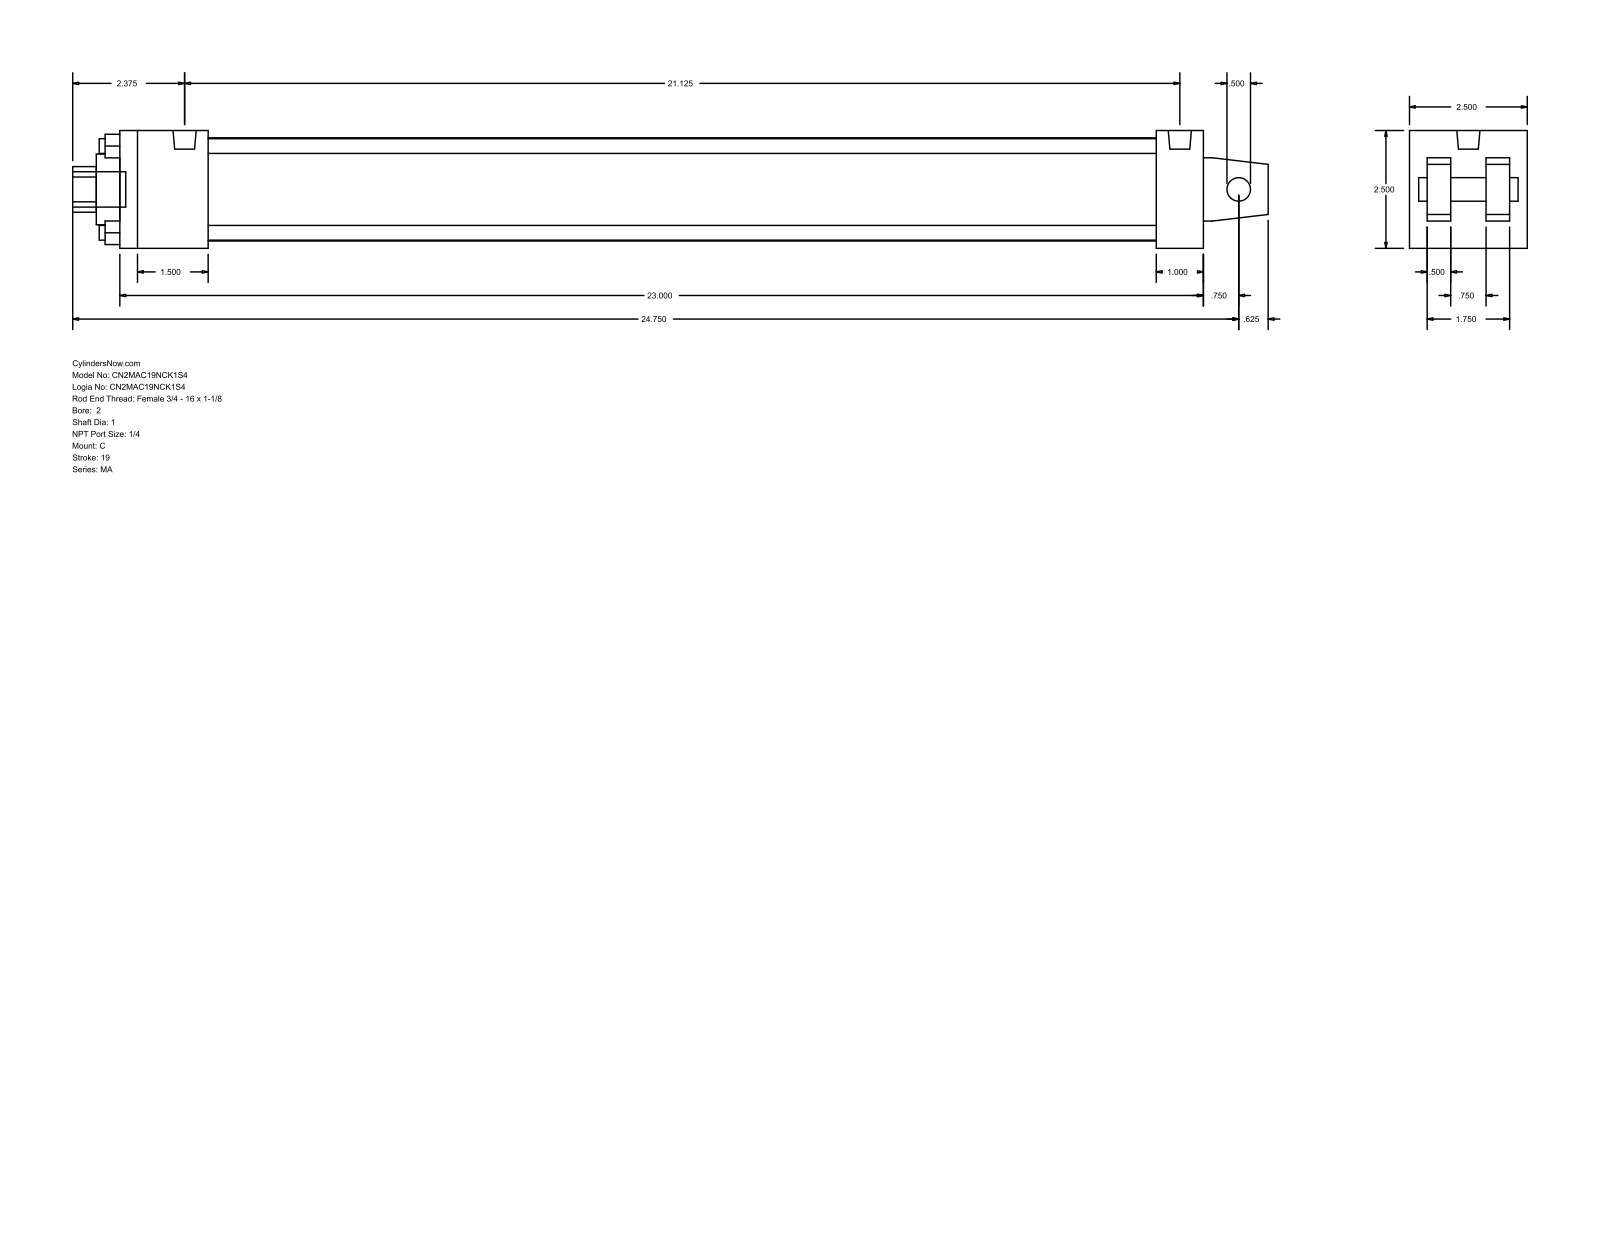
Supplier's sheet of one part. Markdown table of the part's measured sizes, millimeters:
| quantity | value |
| --- | --- |
| part name | MA_C__0200_1 |
| STEP written by | GSSL Pune (CONFIG_CONTROL_DESIGN) |
| units | millimeters |
| bodies | 0 solids, 103 faces (76 planar, 27 cylindrical, 0 other) |
| overall size | 644.52 × 63.5 × 63.5 |
| round holes (diameter × count) | 7.94 × 4, 12.7 × 1, 25.4 × 1, 38.1 × 1, 55.63 × 1 |
| round bosses / shafts (diameter × count) | 7.94 × 4, 12.49 × 2, 19.05 × 1 |
| partial cylindrical surfaces (radius × count) | 12.29 × 1 |
| main face-to-face distances | 63.5, 12.7, 584.2, 22.22, 41.28, 9.52, 53.98, 31.76, 47.63, 25.4 |
| hole center spacings | 33.05, 46.74, 66.1 |
